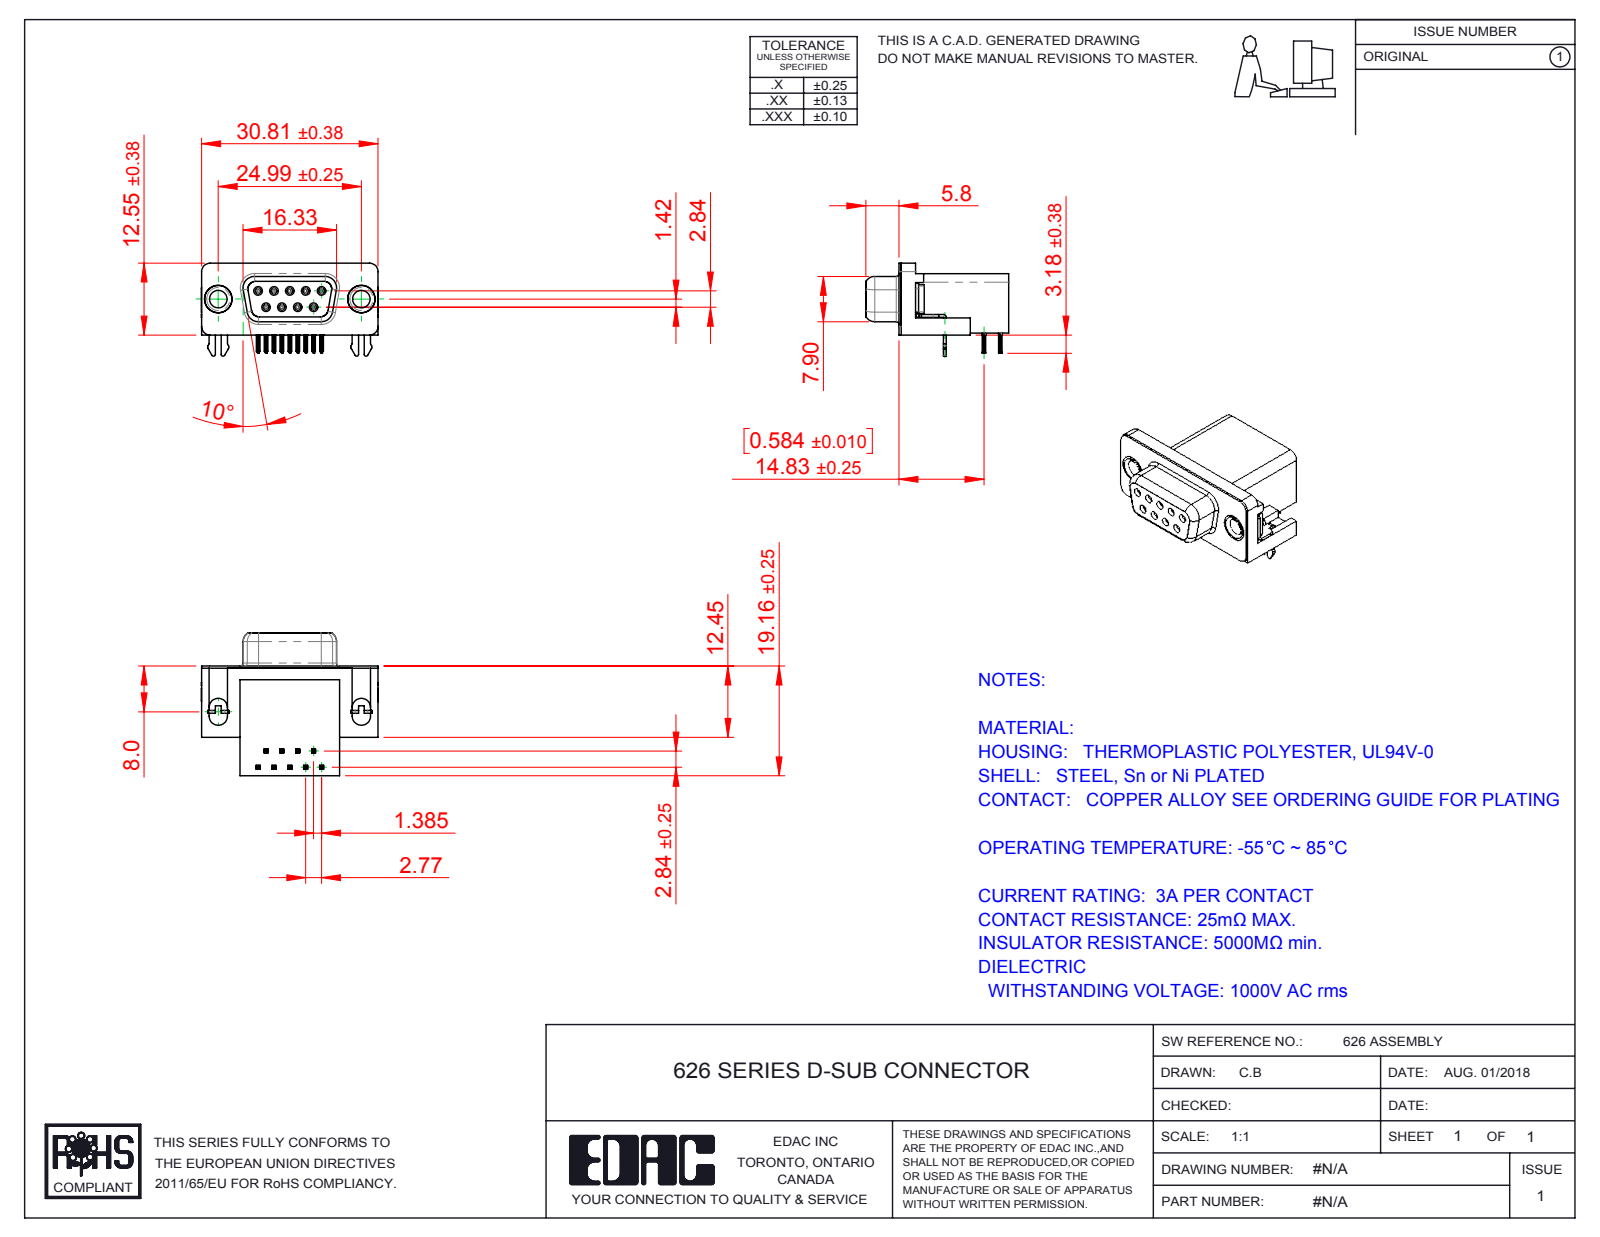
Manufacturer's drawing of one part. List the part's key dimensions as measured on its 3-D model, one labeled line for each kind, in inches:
Part name (STEP PRODUCT): 626 Contact Bottom; 626 Contact Top; 626 Housing_9 Socket; 626 2 Prong Board Lock (+3 more)
STEP written by: SolidWorks 2016 (CONFIG_CONTROL_DESIGN)
Units: inches
Bodies: 15 solids, 1572 faces (716 planar, 406 cylindrical, 450 other)
Overall size (bounding box): 1.216 × 0.983 × 0.64
Volume: 0.302 in³ · Surface area: 8.948 in²
Round holes (diameter × count): ⌀0.031 ×9, ⌀0.035 ×9, ⌀0.12 ×2, ⌀0.157 ×2, ⌀0.189 ×2, ⌀0.197 ×2
Round bosses / shafts (diameter × count): ⌀0.047 ×9, ⌀0.193 ×2, ⌀0.187 ×2, ⌀0.152 ×2
Partial cylindrical surfaces — rounded edges, fillets, slot ends (radius × count): R0.004 ×72, R0.006 ×36, R0.014 ×18, R0.039 ×18, R0.02 ×10, R0.013 ×9, R0.01 ×8, R0.053 ×8
Main face-to-face distances: 0.016, 0.407, 0.014, 0.739, 0.754, 0.114, 0.098, 0.244, 0.64, 0.02
Hole centre spacings: 0.124, 0.109, 0.218, 0.198, 0.198, 0.327, 0.294, 0.295
